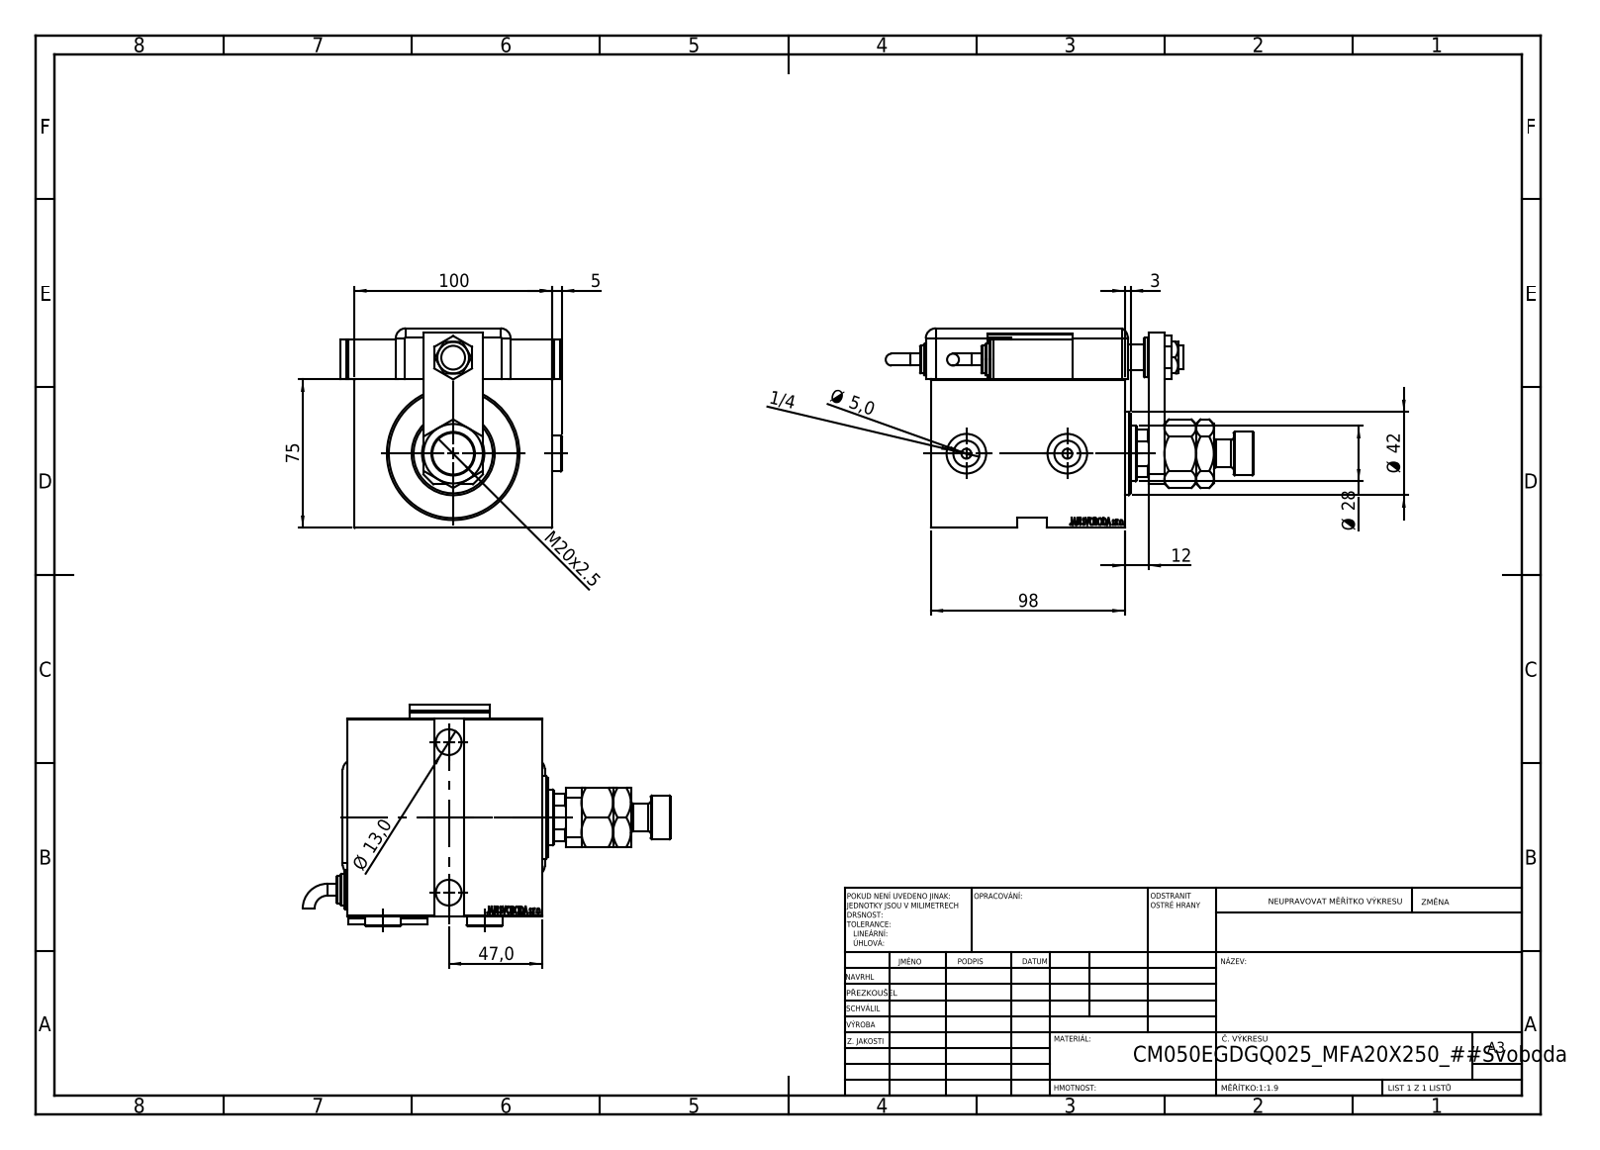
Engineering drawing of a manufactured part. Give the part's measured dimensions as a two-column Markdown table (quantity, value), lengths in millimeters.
| quantity | value |
| --- | --- |
| part name | V450CM_E_VCP; V450CM_VC_B; SWITCH DIM A_G; SWITCH_Q_FRONT_BACK (+8 more) |
| STEP written by | SolidWorks 2019 (CONFIG_CONTROL_DESIGN) |
| units | millimeters |
| bodies | 16 solids, 1338 faces (666 planar, 119 cylindrical, 553 other) |
| overall size | 185.76 × 111.9 × 100.8 |
| volume | 838 708 mm³ |
| surface area | 161 201 mm² |
| round holes (diameter × count) | 13 × 3, 20 × 3, 4 × 2, 5 × 2, 8 × 2, 13.16 × 2, 19 × 2, 12 × 1, 14 × 1, 18.5 × 1, 28 × 1, 31.5 × 1 |
| round bosses / shafts (diameter × count) | 20 × 3, 14 × 3, 18 × 2, 16 × 2, 6 × 2, 52 × 1, 42 × 1, 22 × 1 |
| partial cylindrical surfaces (radius × count) | 5 × 9, 10 × 1, 13.5 × 1 |
| main face-to-face distances | 3, 75, 98, 100, 14, 20, 84, 79, 25, 100.8 |
| hole center spacings | 47.2, 61.22, 20, 48.5, 51, 76 |
